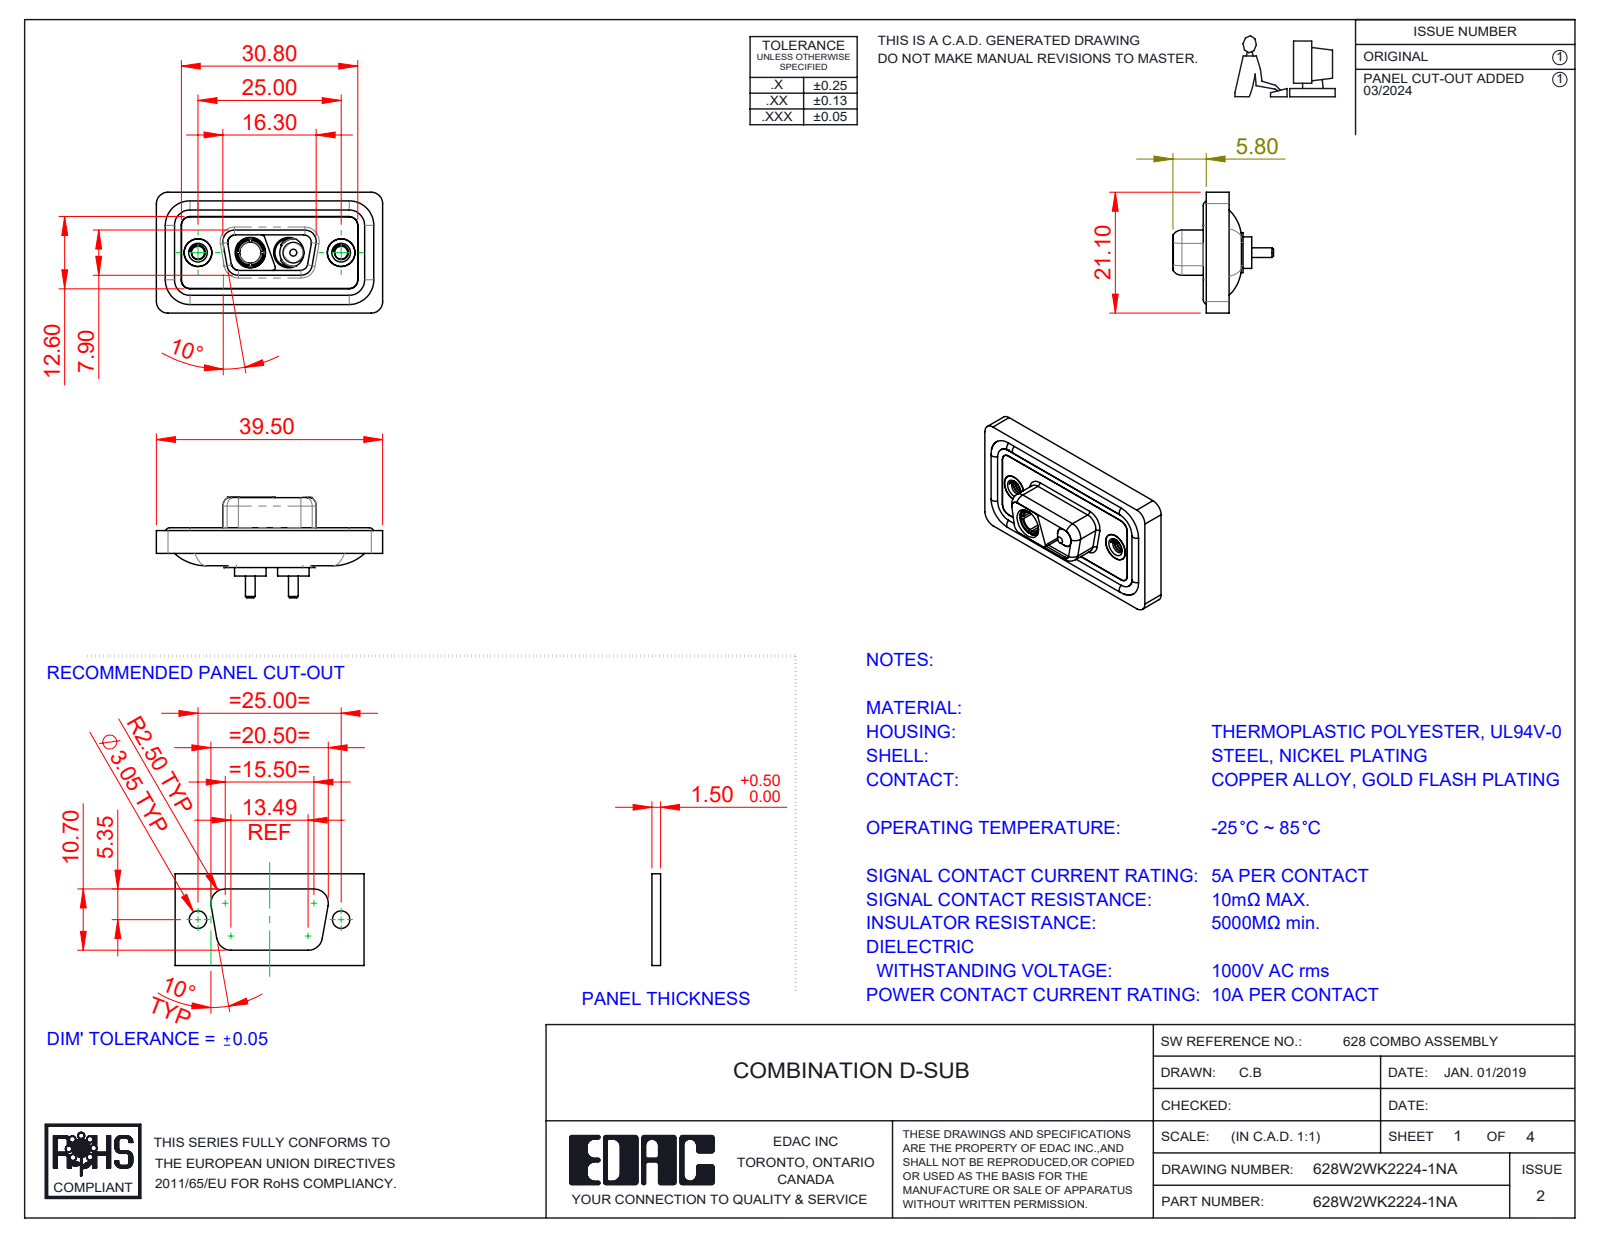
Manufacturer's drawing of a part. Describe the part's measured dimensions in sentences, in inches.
The part is named "628Combo Shell Rear_09 Contacts; 628Combo Housing_2WK2; 628Combo Threaded Rivet_A; Power Socket_10A S (+4 more)". Its 3-D file was written by "SolidWorks 2023 (CONFIG_CONTROL_DESIGN)". It is 11 solids with 498 faces: 144 planar, 233 cylindrical and 121 other. Overall it measures 1.555 by 0.831 by 0.691 inches. Its volume is 0.279 cubic inches and its surface area 11.34 square inches. Round holes: 4 of diameter 0.191, 2 of diameter 0.089, 2 of diameter 0.157, 2 of diameter 0.159, 2 of diameter 0.197, 2 of diameter 0.209, 1 of diameter 0.146. Round bosses or shafts: 4 of diameter 0.063, 2 of diameter 0.217, 2 of diameter 0.205, 2 of diameter 0.195, 2 of diameter 0.189, 2 of diameter 0.187, 2 of diameter 0.148, 2 of diameter 0.067. Partial cylindrical surfaces (rounded edges, fillets, slot ends): 22 of radius 0.059, 18 of radius 0.079, 8 of radius 0.053, 8 of radius 0.063, 6 of radius 0.02, 4 of radius 0.01, 4 of radius 0.024, 4 of radius 0.026. The main face-to-face distances are 0.016, 0.043, 0.114, 0.063, 0.02, 0.071, 0.222, 0.059, 0.211, 0.122. The hole center spacings are 0.36, 0.624, 0.265, 0.984.
